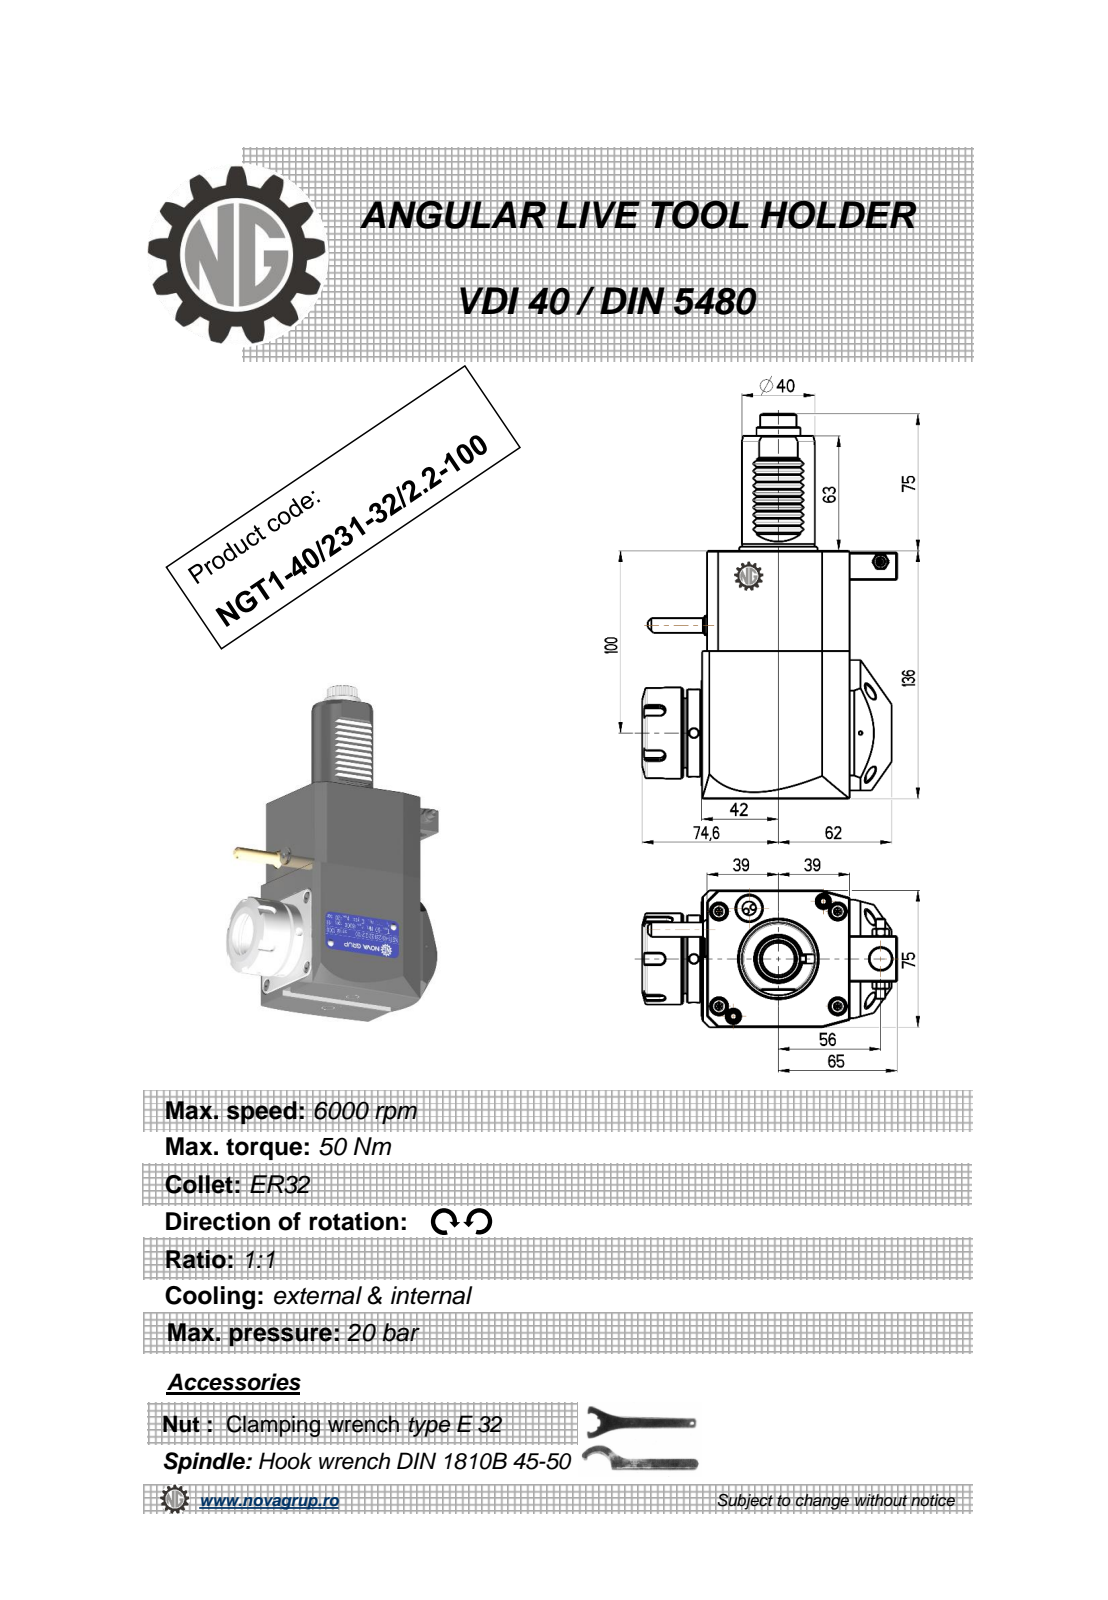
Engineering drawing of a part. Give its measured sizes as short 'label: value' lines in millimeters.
name: NGT1_40_231_32_2_2_100
written by: PRO/ENGINEER BY PARAMETRIC TECHNOLOGY CORPORATION, 2010280 (CONFIG_CONTROL_DESIGN)
unit: mm
bodies: 1 solid, 531 faces (193 planar, 185 cylindrical, 153 other)
size: 211 × 139.6 × 76.6
volume: 1 009 000 mm³; area: 76 806 mm²
holes: 3× ⌀5, 1× ⌀3, 1× ⌀4.2, 1× ⌀9.5, 1× ⌀12, 1× ⌀27
bosses: 1× ⌀50, 1× ⌀48, 1× ⌀41, 1× ⌀40, 1× ⌀24, 1× ⌀11.2, 1× ⌀8.96, 1× ⌀8
rounds: 48× R2.08, 12× R0.26, 10× R0.3, 6× R0.22, 5× R3, 1× R9.08, 1× R9.92, 1× R15
face distances: 75, 136, 78, 3, 81, 2.8, 80.8, 4.5, 7.5, 0.5
hole spacings: 36.22, 61.13, 91.5, 102.25, 138.89
